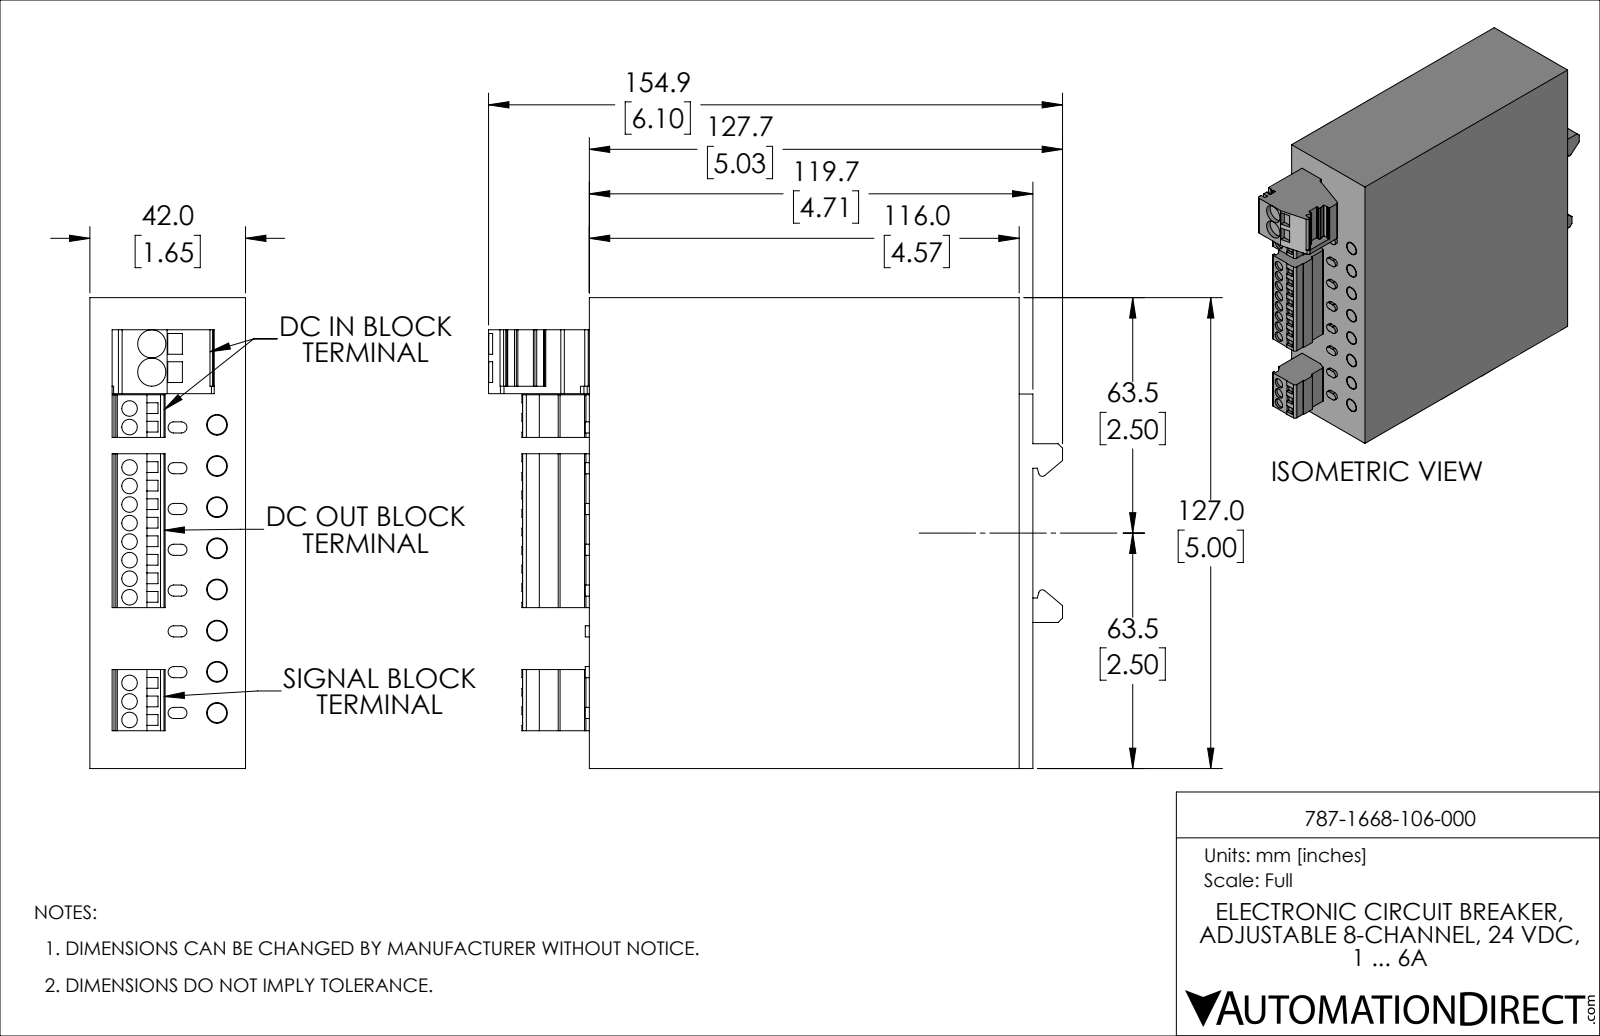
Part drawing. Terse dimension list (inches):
name: 787-1668/106-000
written by: PARTsolutions (CONFIG_CONTROL_DESIGN)
unit: in
bodies: 1 solid, 366 faces (281 planar, 85 cylindrical, 0 other)
size: 6.098 × 5 × 1.654
volume: 40.26 in³; area: 93.23 in²
holes: 13× ⌀0.165, 8× ⌀0.22, 2× ⌀0.299
bosses: 8× ⌀0.205
rounds: 16× R0.059, 12× R0.008, 9× R0.039, 4× R0.016, 2× R0.012, 2× R0.019
face distances: 1.654, 5, 4.713, 0.146, 4.567, 0.236, 1.417, 0.199, 1.455, 1.02
hole spacings: 0.197, 0.394, 0.437, 0.874, 0.591, 1.311, 0.787, 1.748
